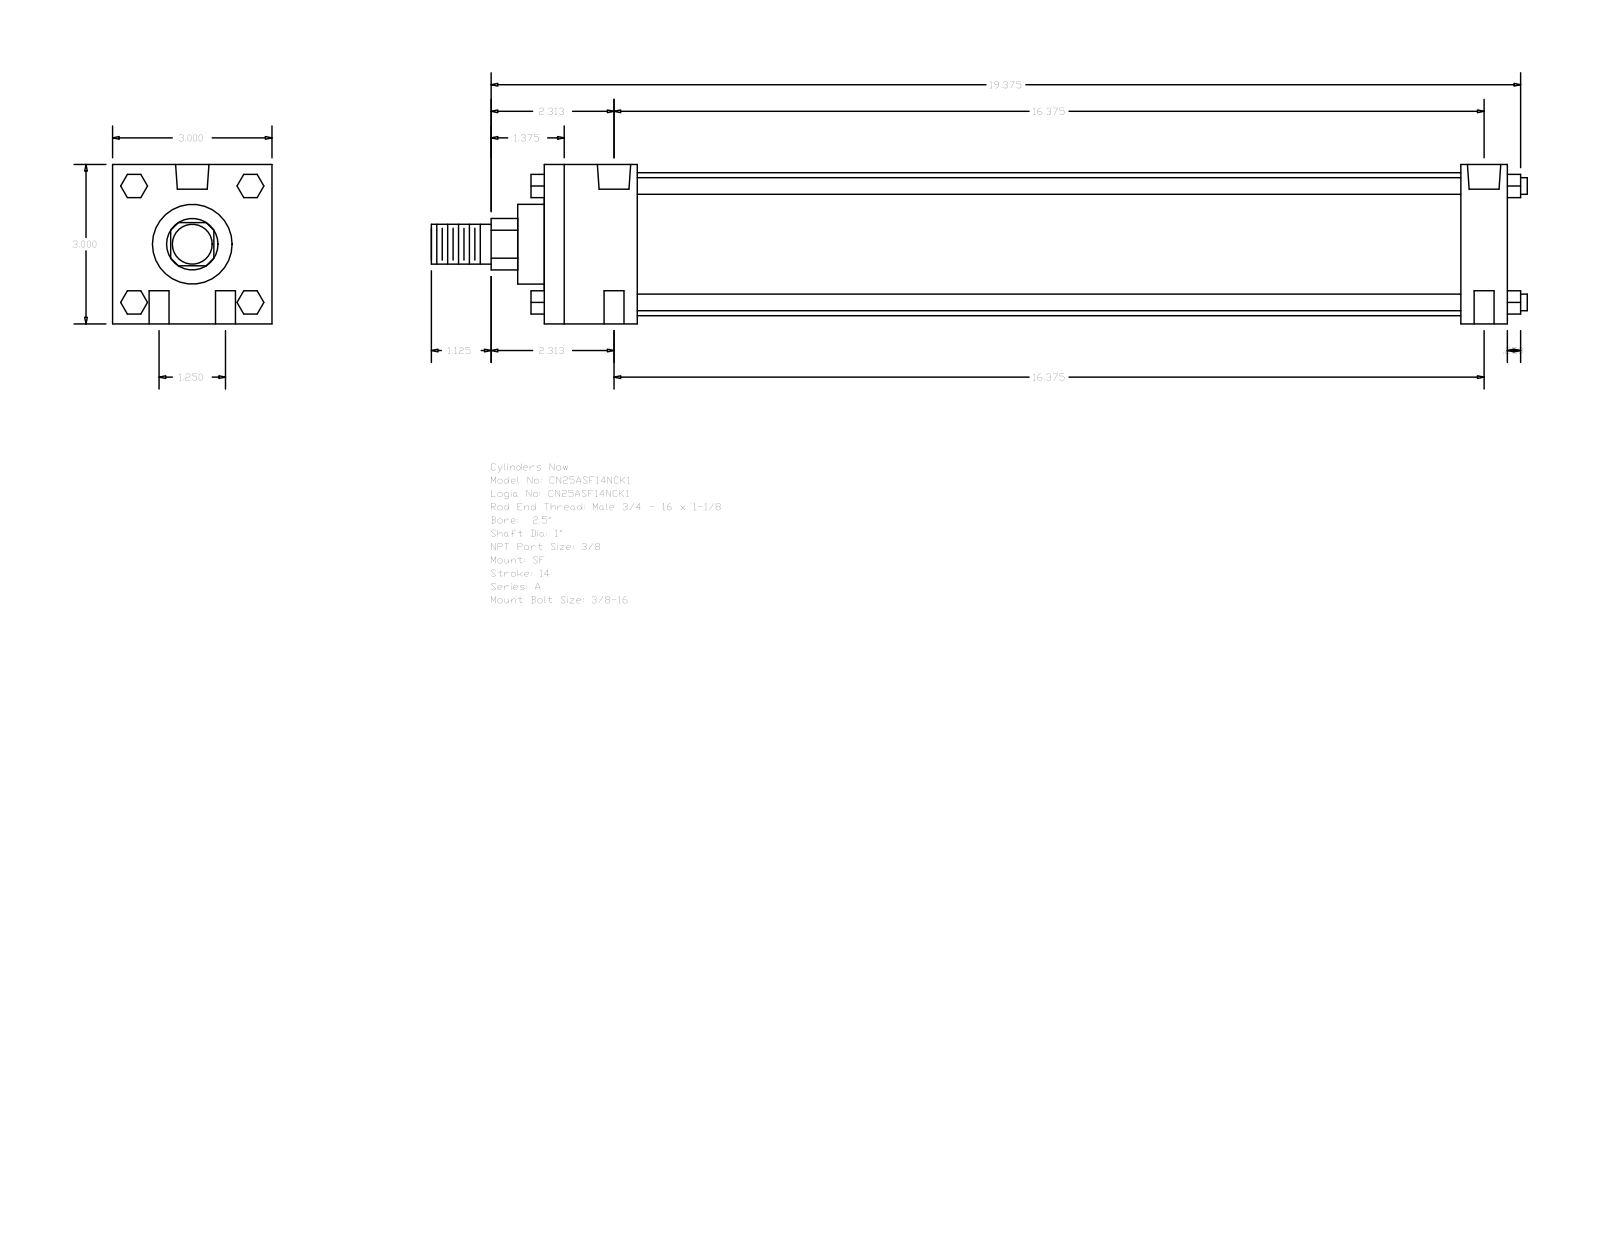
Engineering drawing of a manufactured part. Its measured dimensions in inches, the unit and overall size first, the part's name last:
Units: inches
Overall size (bounding box): 20.625 × 3 × 3
Round holes (diameter × count): ⌀0.375 ×4, ⌀0.219 ×2, ⌀0.627 ×2
Round bosses / shafts (diameter × count): ⌀0.313 ×4, ⌀2.69 ×1, ⌀1.5 ×1, ⌀1 ×1, ⌀0.75 ×1
Partial cylindrical surfaces — rounded edges, fillets, slot ends (radius × count): R0.484 ×1
Main face-to-face distances: 3, 18.125, 17.25, 0.875, 1.75, 15.5, 16.375, 0.5, 18.625, 0.25
Hole centre spacings: 0.625, 16.387, 16.375, 1.25, 16.422, 16.562
Bodies: 0 solids, 124 faces (94 planar, 30 cylindrical, 0 other)
Part name (STEP PRODUCT): A_SF__0250_1
STEP written by: GSSL Pune (CONFIG_CONTROL_DESIGN)
